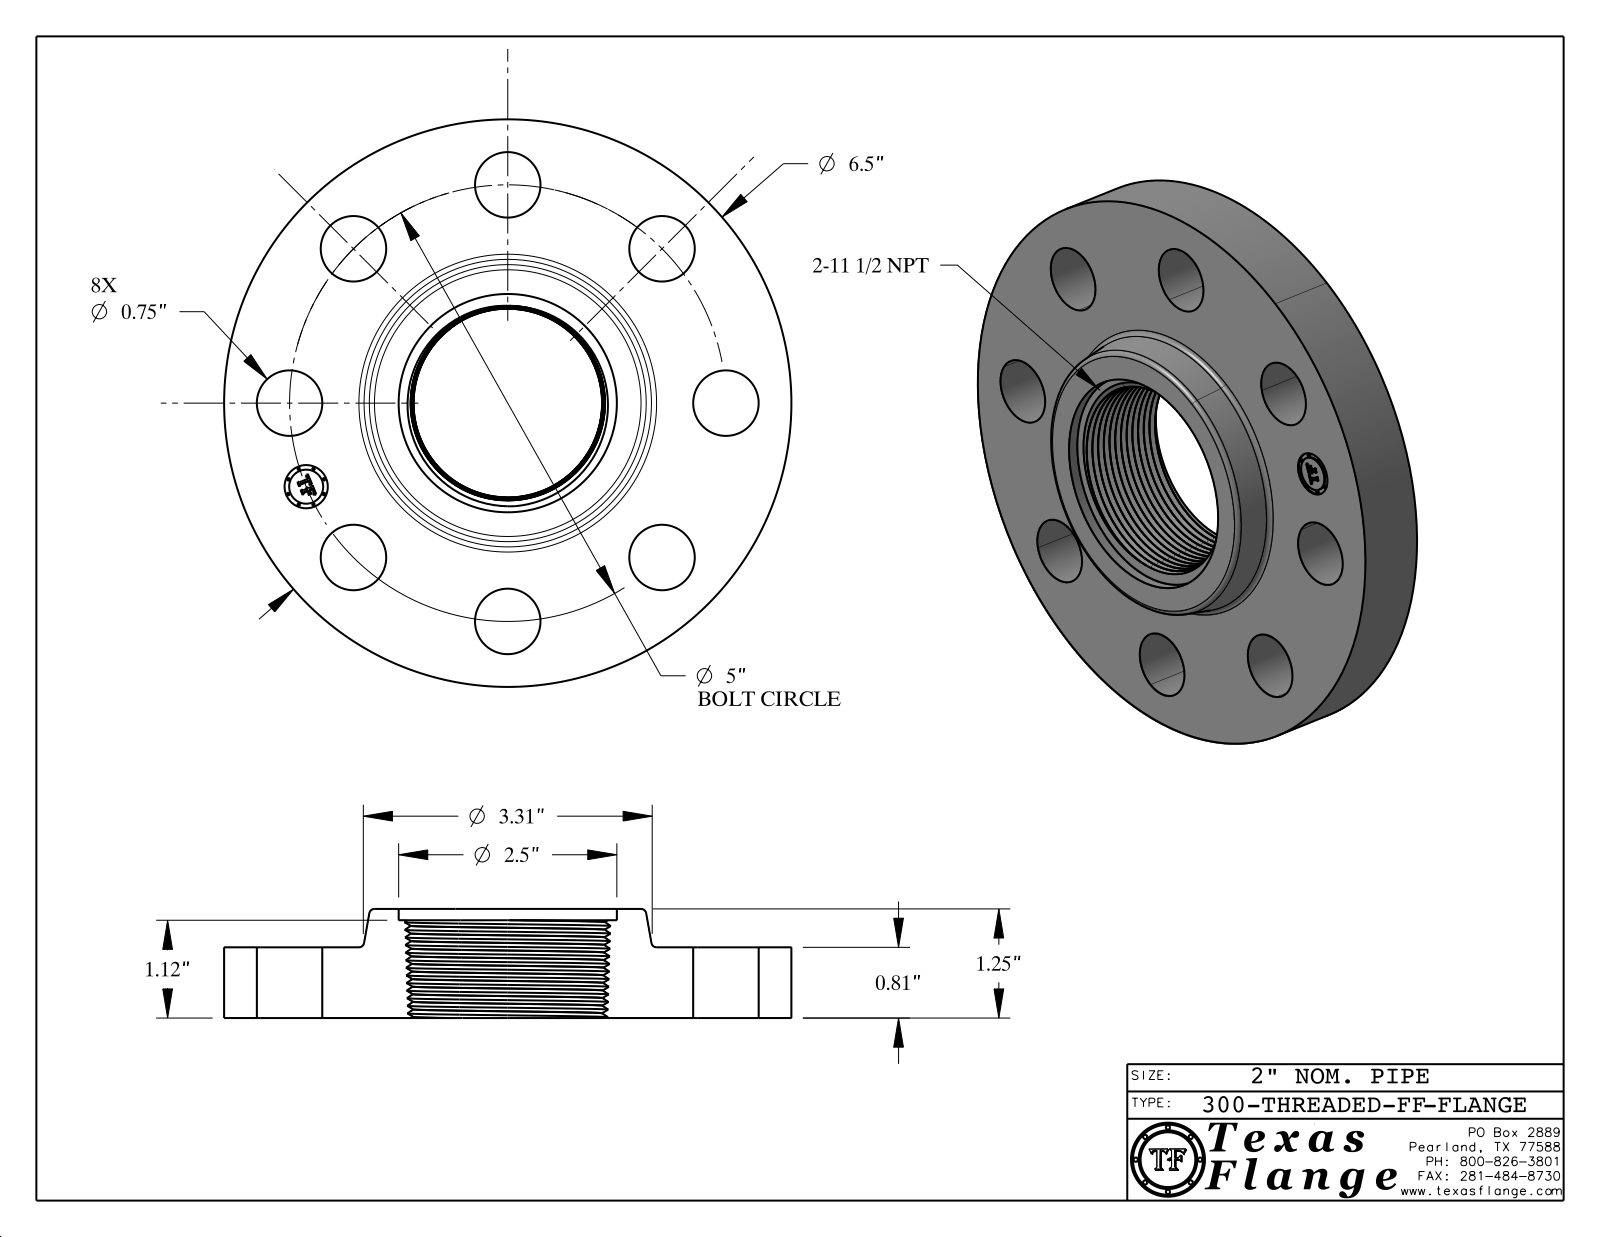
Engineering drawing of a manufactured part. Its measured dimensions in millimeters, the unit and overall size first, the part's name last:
Units: millimetres
Overall size (bounding box): 165.1 × 165.1 × 31.8
Round holes (diameter × count): ⌀19.1 ×8, ⌀12.6 ×1, ⌀63.5 ×1
Round bosses / shafts (diameter × count): ⌀0.8 ×8, ⌀165.1 ×1, ⌀9.9 ×1
Main face-to-face distances: 20.6, 31.8, 11.2, 28.4, 7.9, 3.3, 20.2, 0.4, 8.3, 11.6
Hole centre spacings: 63.5, 48.6, 89.8, 117.3, 127, 24.8, 70.6, 105.6
Volume: 368 500 mm³ · Surface area: 66 130 mm²
Bodies: 1 solid, 548 faces (369 planar, 40 cylindrical, 139 other)
Part name (STEP PRODUCT): 300-THREADED-FF
STEP written by: CATIA V5 STEP AP214 (AUTOMOTIVE_DESIGN)
